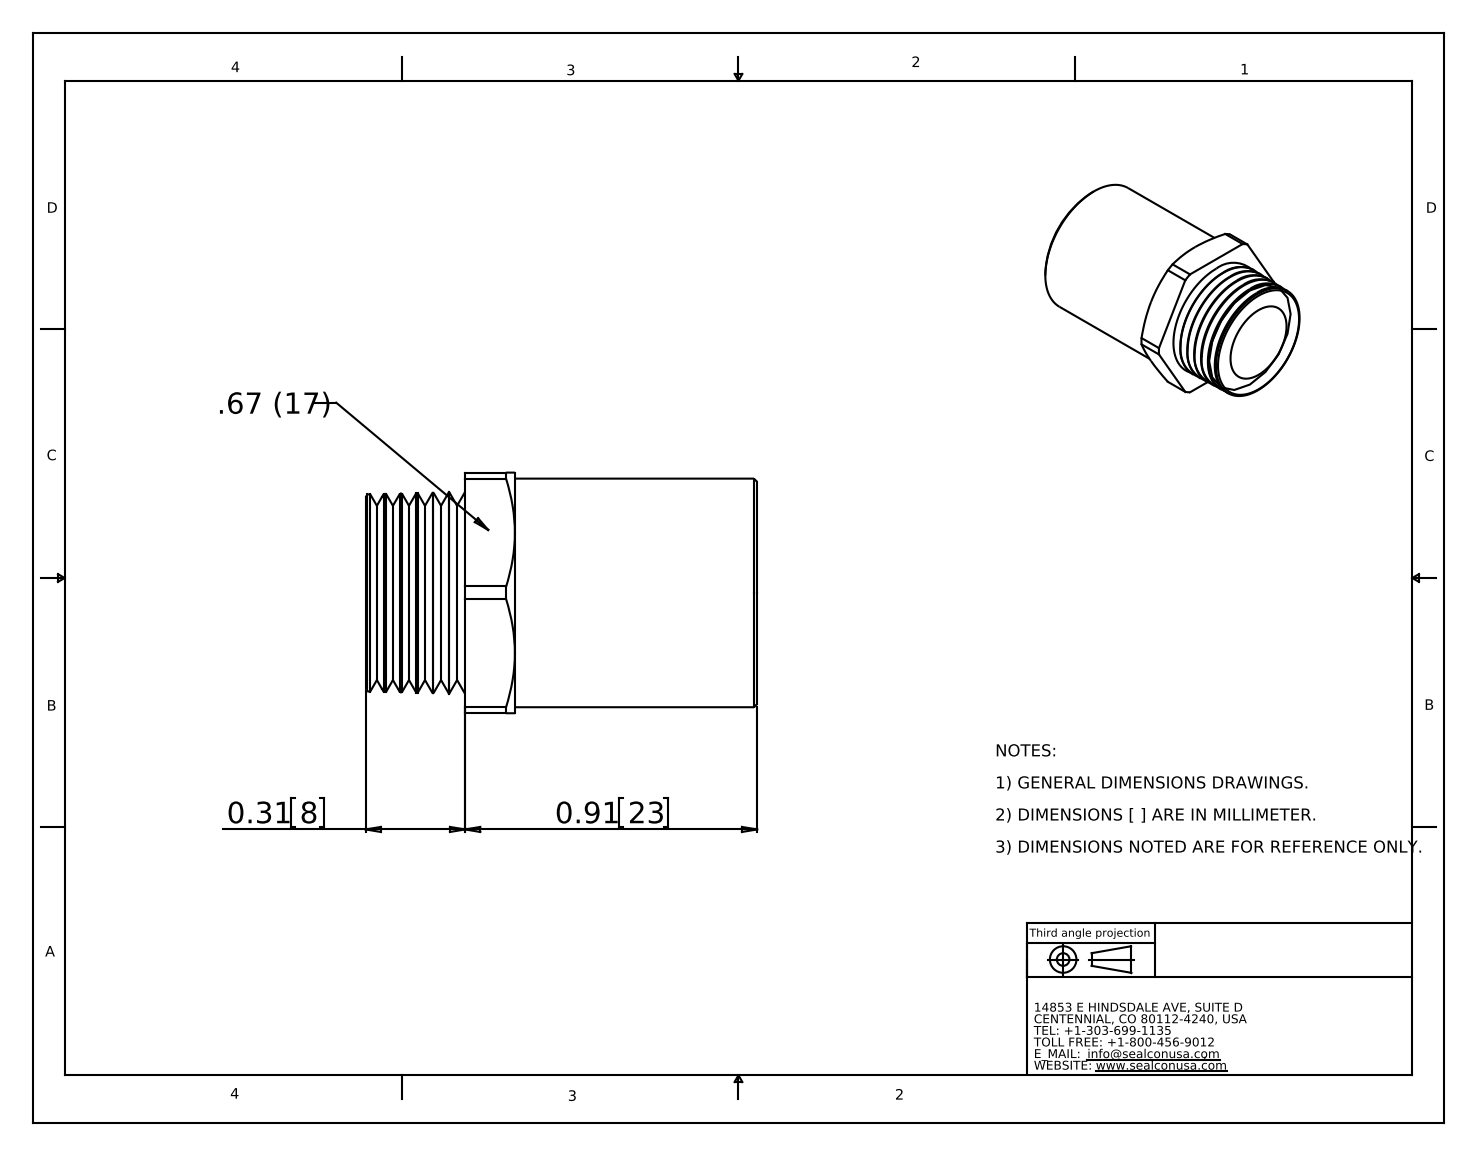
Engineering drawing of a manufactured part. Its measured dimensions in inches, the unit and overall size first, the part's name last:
Units: inches
Overall size (bounding box): 1.22 × 0.844 × 0.75
Round holes (diameter × count): ⌀0.48 ×1
Round bosses / shafts (diameter × count): ⌀0.713 ×1
Partial cylindrical surfaces — rounded edges, fillets, slot ends (radius × count): R0.422 ×1
Main face-to-face distances: 0.91, 1.22, 0.31, 0.755, 0.155, 0.465, 0.75, 0.75
Volume: 0.271 in³ · Surface area: 5.54 in²
Bodies: 1 solid, 71 faces (11 planar, 11 cylindrical, 49 other)
Part name (STEP PRODUCT): SM16MA-BK
STEP written by: SolidWorks 2007 (AUTOMOTIVE_DESIGN)
